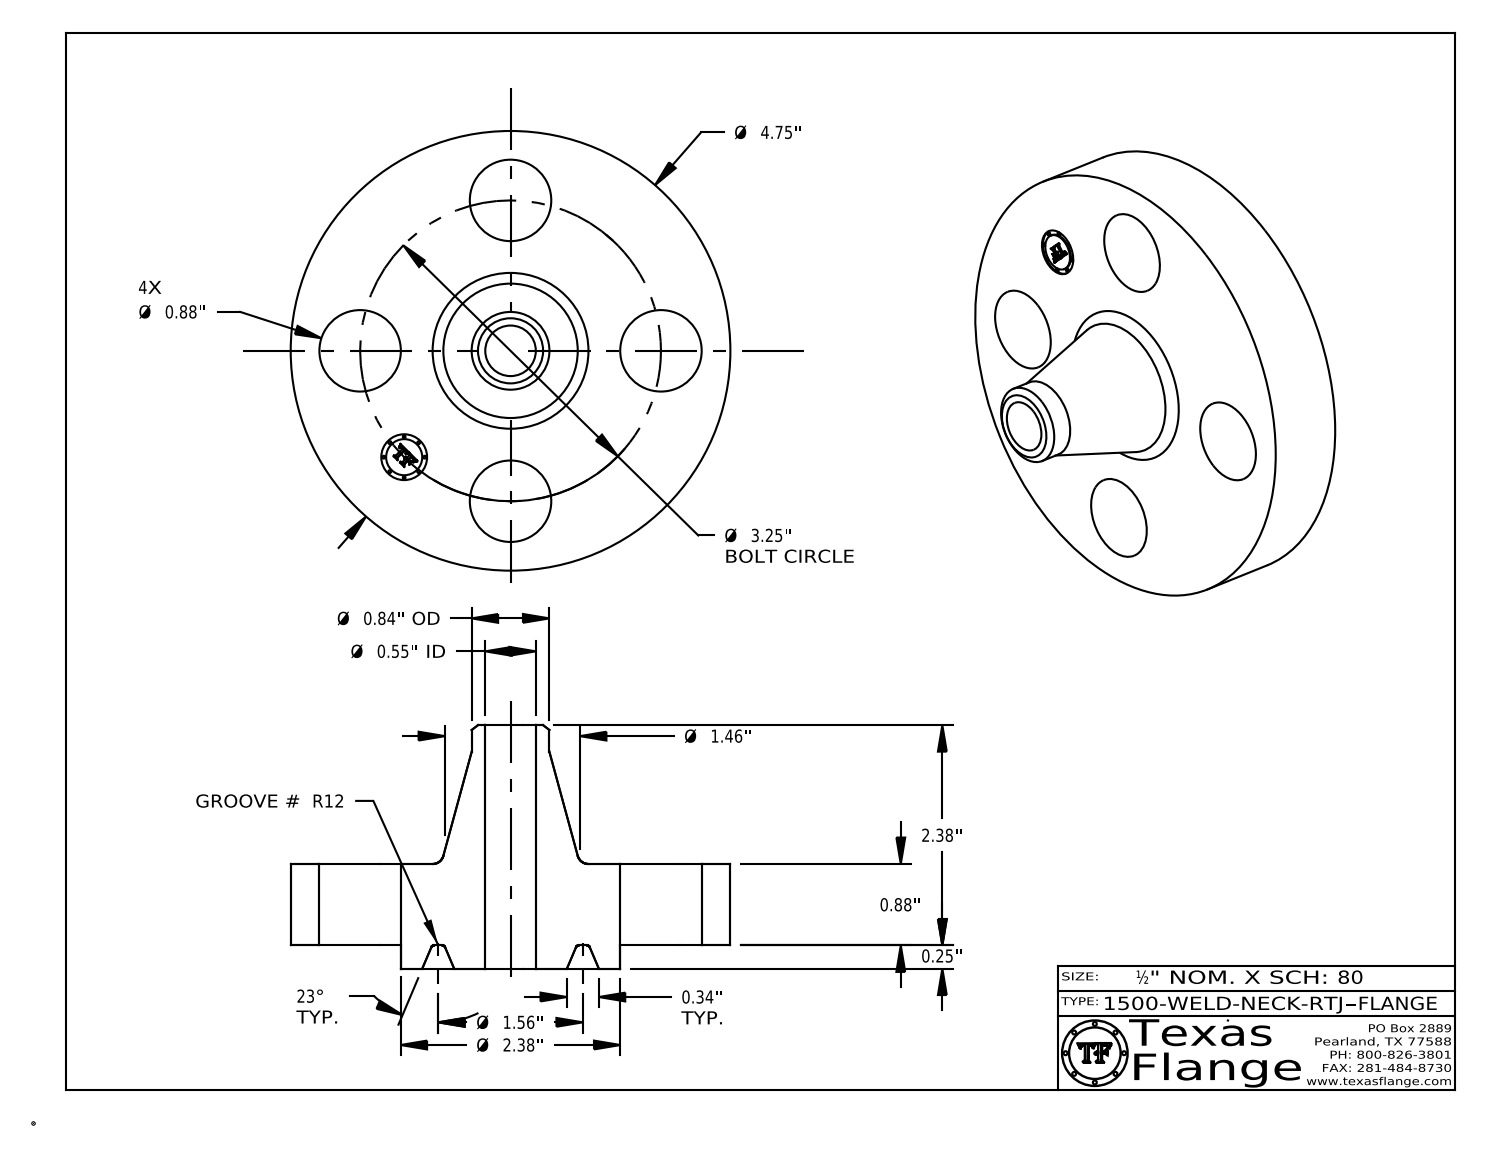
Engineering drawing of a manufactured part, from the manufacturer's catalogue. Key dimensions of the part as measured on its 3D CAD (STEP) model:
Part name (STEP PRODUCT): 1500-WELD-NECK-RTJ
STEP written by: CATIA V5 STEP AP214 (AUTOMOTIVE_DESIGN)
Units: inches
Bodies: 1 solid, 425 faces (371 planar, 40 cylindrical, 14 other)
Overall size (bounding box): 4.75 × 4.75 × 2.63
Volume: 15.15 in³ · Surface area: 64.96 in²
Round holes (diameter × count): ⌀0.88 ×4, ⌀0.495 ×1, ⌀0.546 ×1
Round bosses / shafts (diameter × count): ⌀0.03 ×8, ⌀4.75 ×1, ⌀2.375 ×1, ⌀0.84 ×1, ⌀0.39 ×1
Main face-to-face distances: 0.88, 0.25, 1.13, 2.63, 2.38, 1.5, 1.115, 0.865, 0.015, 1.515
Hole centre spacings: 1.625, 2.298, 1.244, 3.003, 3.25
